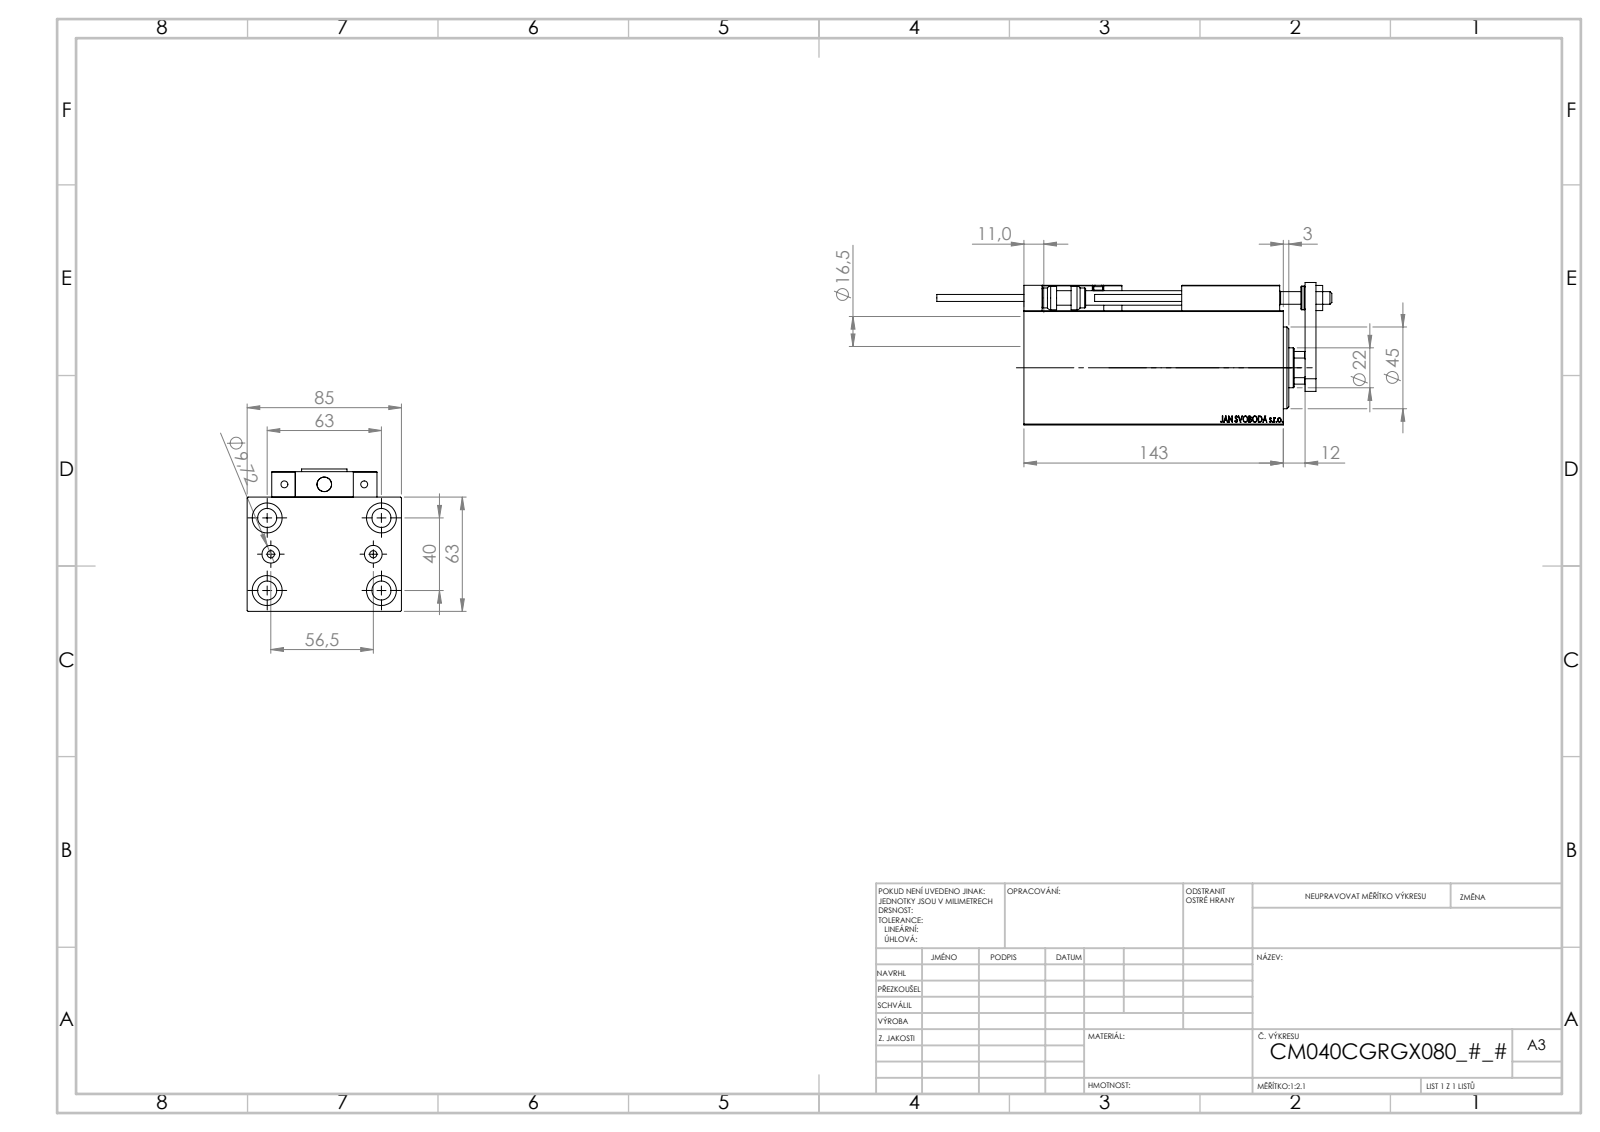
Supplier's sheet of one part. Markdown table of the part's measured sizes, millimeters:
| quantity | value |
| --- | --- |
| part name | MAGNET; ZARAZKA; ALLEN BOLT D8; SWITCH DIM B,W (+7 more) |
| STEP written by | SolidWorks 2019 (CONFIG_CONTROL_DESIGN) |
| units | millimeters |
| bodies | 23 solids, 1278 faces (560 planar, 184 cylindrical, 534 other) |
| overall size | 217.7 × 85 × 78.5 |
| volume | 686 488 mm³ |
| surface area | 142 479 mm² |
| round holes (diameter × count) | 4 × 6, 8 × 5, 16.5 × 5, 3.2 × 4, 10.5 × 4, 5 × 2, 9.72 × 2, 7 × 1, 12.5 × 1, 22 × 1, 25.5 × 1, 40 × 1 |
| round bosses / shafts (diameter × count) | 5 × 2, 3.8 × 2, 13 × 1, 11 × 1 |
| partial cylindrical surfaces (radius × count) | 0.3 × 30, 3 × 2, 10.5 × 1 |
| main face-to-face distances | 63, 85, 12, 143, 131, 14, 77, 18, 6, 1 |
| hole center spacings | 20.26, 37.31, 63.01, 11.37, 20, 28.25, 29.59, 29.69 |
